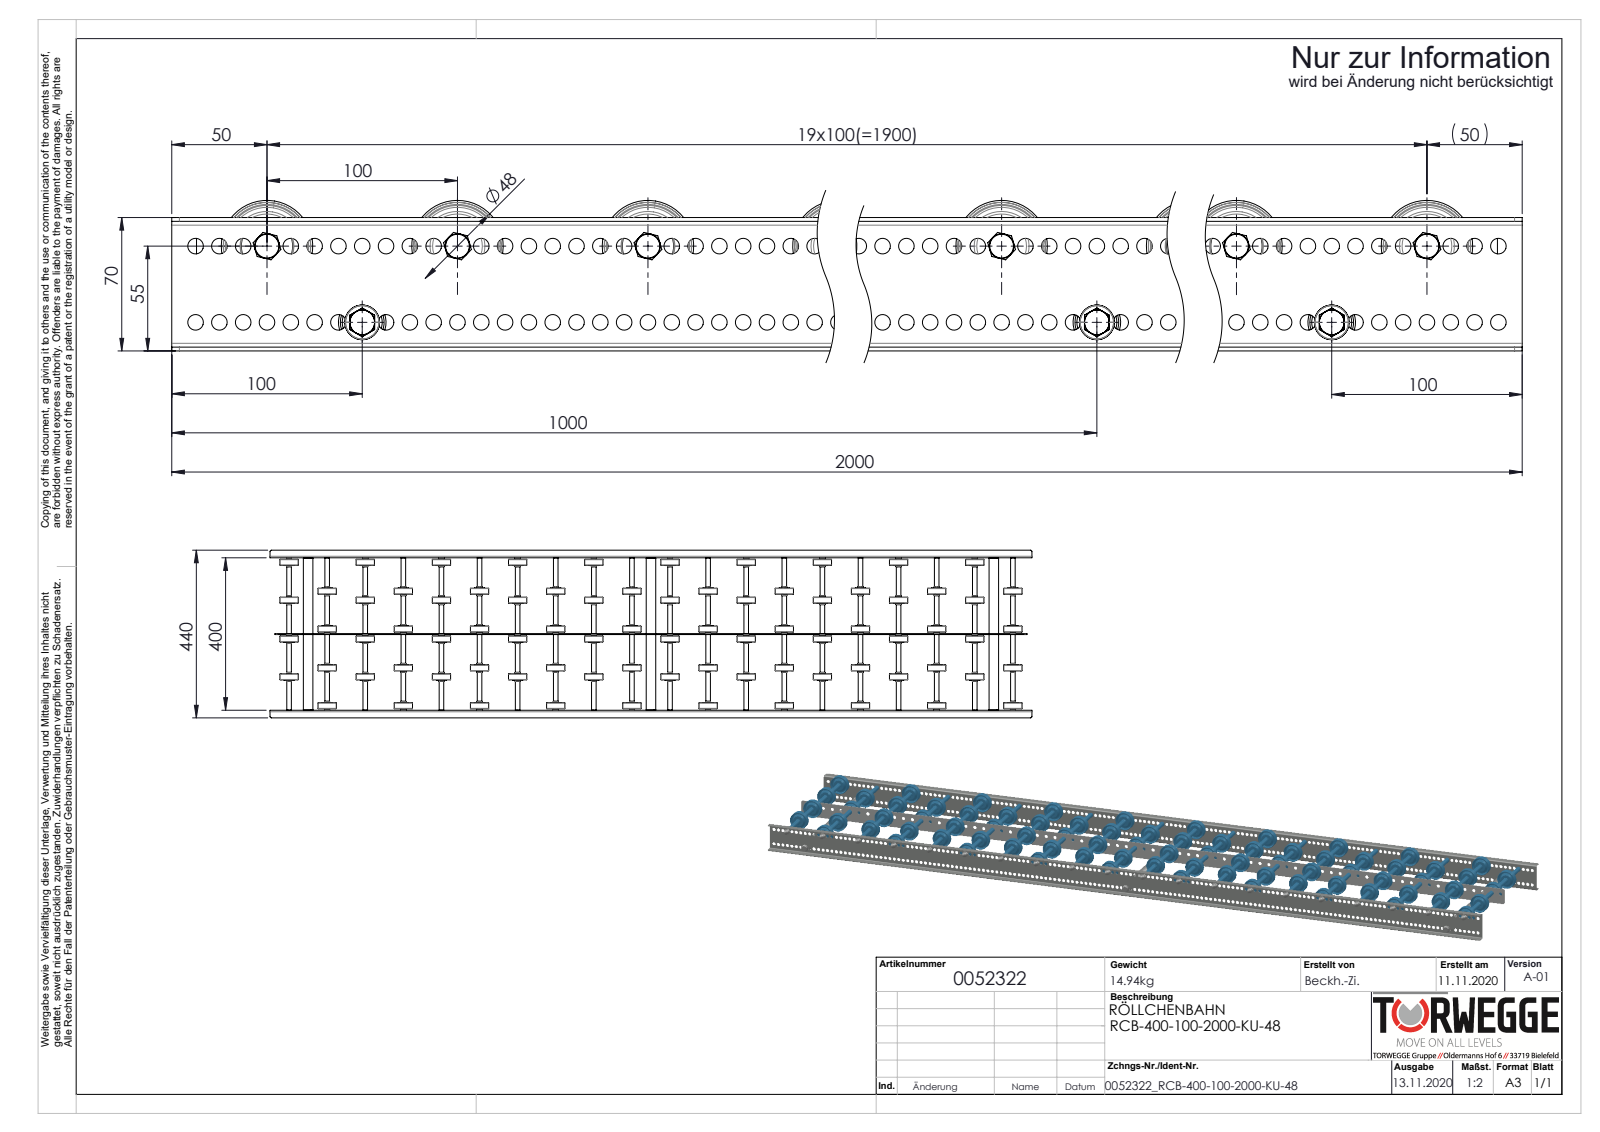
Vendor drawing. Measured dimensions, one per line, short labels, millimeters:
name: 0052322; S106837_Gewindestange-M8-KFG_L420; Röllchenachse-für-Konfiguration_EL400; 0011532_2300-48-8 (+6 more)
written by: SolidWorks 2020 (AUTOMOTIVE_DESIGN)
unit: mm
bodies: 238 solids, 9114 faces (1568 planar, 3470 cylindrical, 4076 other)
size: 2000 × 440 × 79
volume: 3 399 000 mm³; area: 2 608 000 mm²
holes: 318× ⌀8.2, 79× ⌀8.5, 20× ⌀6.65, 20× ⌀9.65, 20× ⌀13.7, 3× ⌀6.8, 3× ⌀21
bosses: 23× ⌀8, 20× ⌀48, 20× ⌀27, 20× ⌀12.7, 20× ⌀12.5, 20× ⌀12, 3× ⌀25
rounds: 8× R4, 4× R2, 4× R5
face distances: 2, 402, 68, 404, 400, 201.1, 198.6, 200.9, 198.9, 203.1
hole spacings: 12.5, 25, 37.5, 50, 62.5, 75, 87.5, 100
